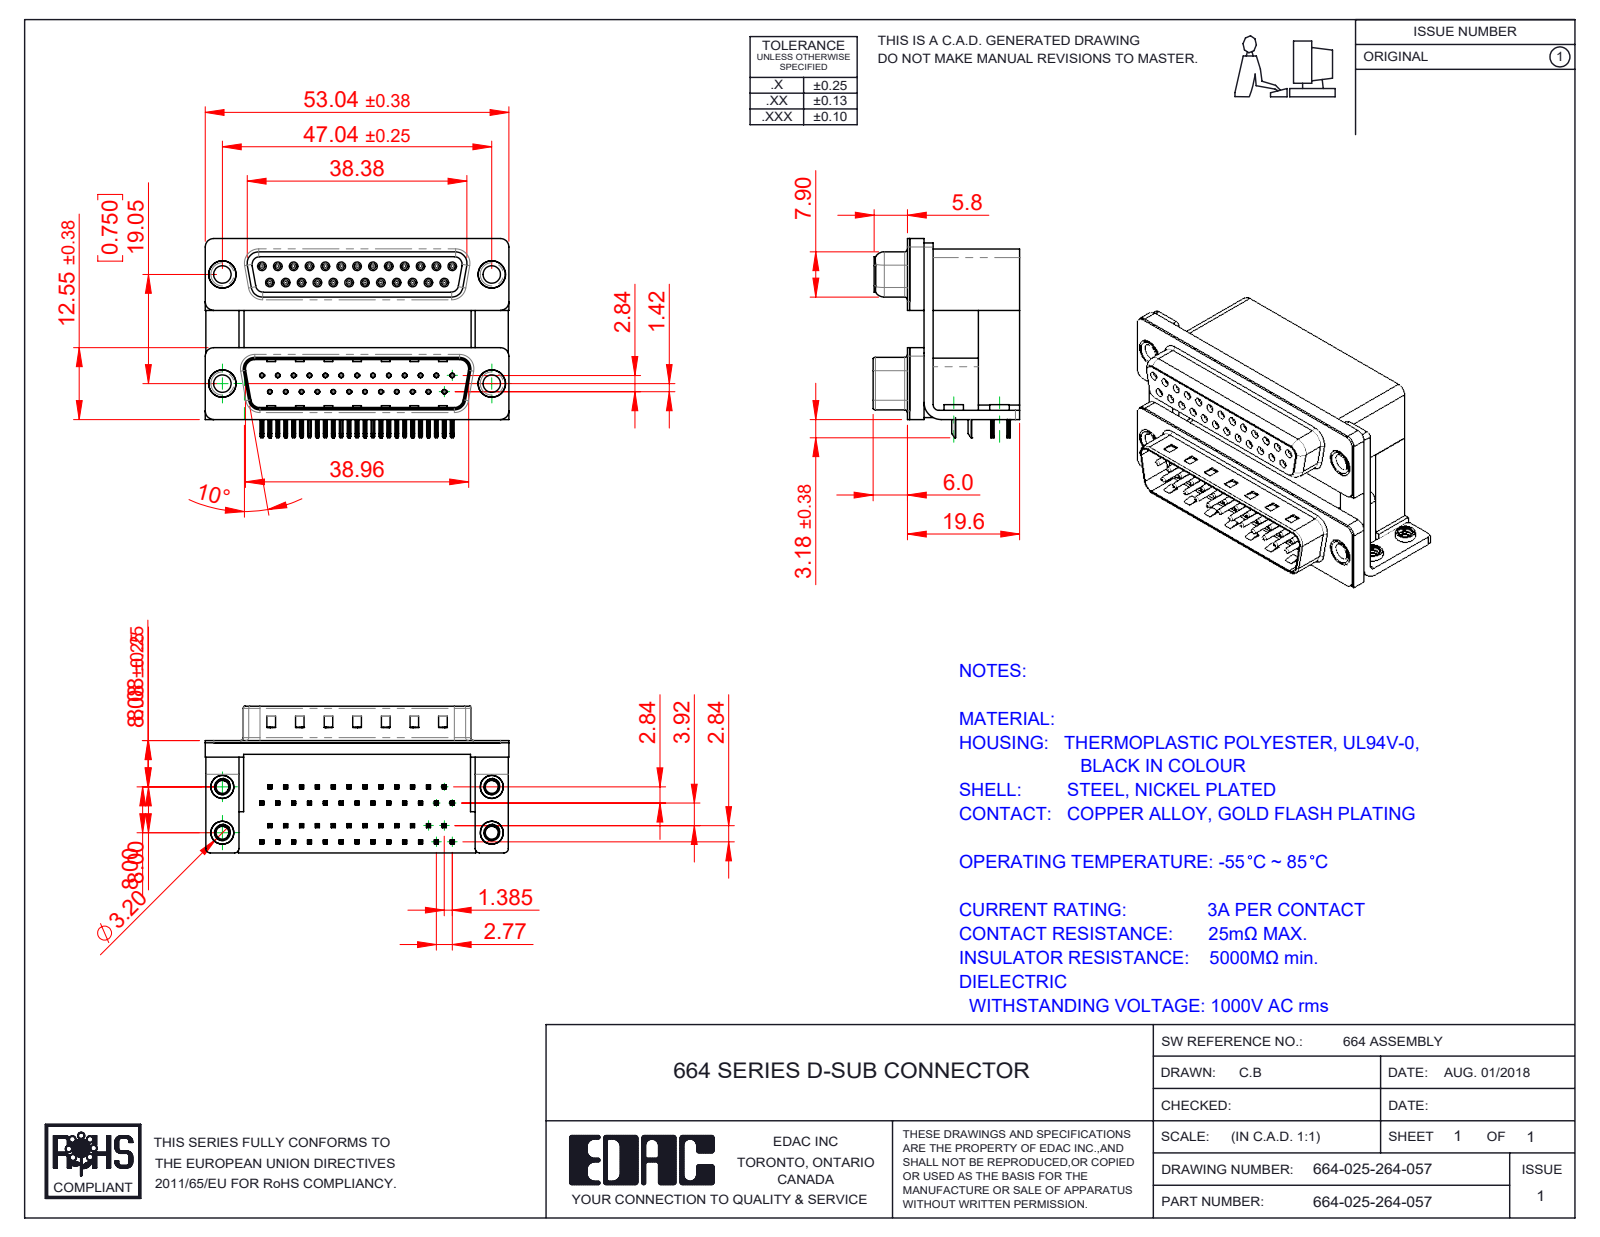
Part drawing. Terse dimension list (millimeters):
name: 664 Housing Upper_25 Contacts M; 664 Contact Top Lower; 664 Mounting Bracket_ThruM; 664 Contact Bottom Lower (+8 more)
written by: SolidWorks 2020 (CONFIG_CONTROL_DESIGN)
unit: mm
bodies: 65 solids, 6259 faces (3269 planar, 1583 cylindrical, 1407 other)
size: 53.04 × 34.78 × 25.6
volume: 22 499 mm³; area: 24 270 mm²
holes: 50× ⌀0.8, 25× ⌀0.35, 25× ⌀0.9, 4× ⌀2.26, 4× ⌀2.75, 4× ⌀3.05, 4× ⌀3.2, 4× ⌀3.5, 4× ⌀4, 4× ⌀4.8, 4× ⌀5
bosses: 25× ⌀1.2, 25× ⌀0.75, 4× ⌀4.9, 4× ⌀4.75, 4× ⌀4, 4× ⌀3.85, 4× ⌀3.4
rounds: 200× R0.1, 100× R0.15, 100× R0.25, 50× R0.12, 50× R0.35, 25× R0.34, 14× R1.5, 12× R0.28
face distances: 0.4, 19.2, 7.2, 12, 10.69, 16.7, 9.5, 2.5, 2.84, 18.71
hole spacings: 2.77, 3.16, 5.54, 8.31, 11.08, 13.85, 16.62, 5.03
